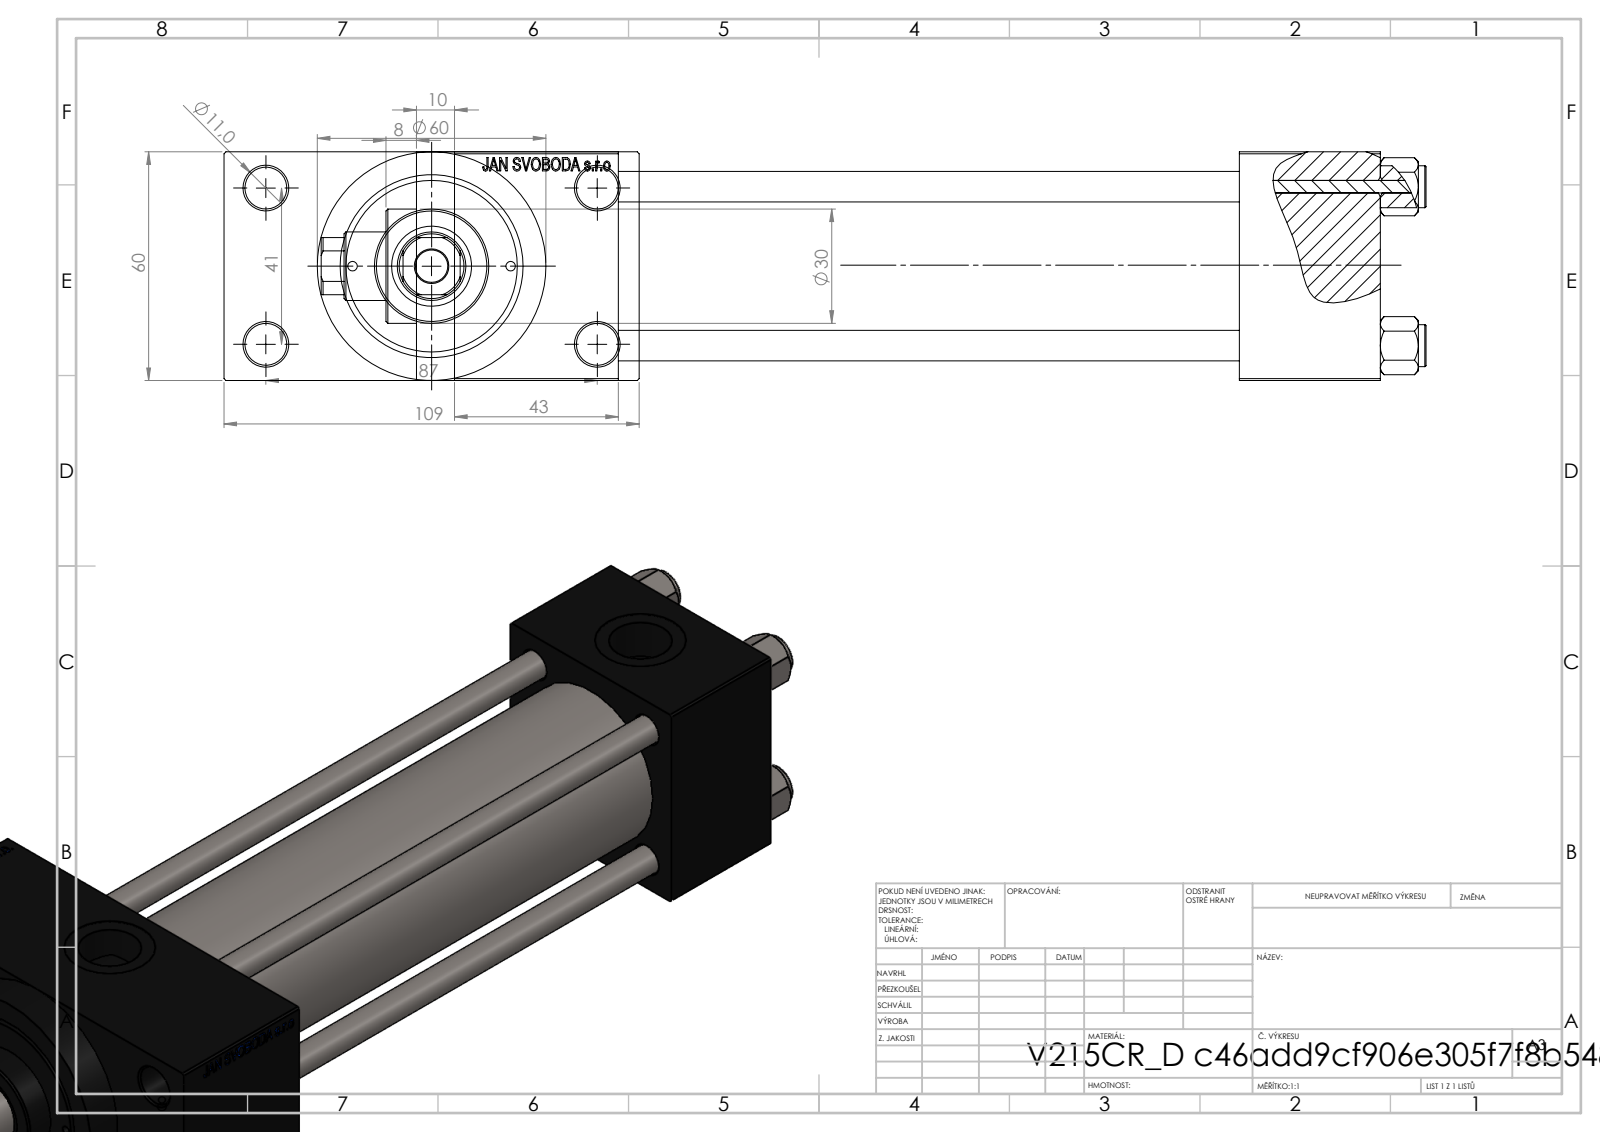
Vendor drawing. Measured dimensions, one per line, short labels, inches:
name: V215CR_VCP_D; V215CR_D_TYCINKA; NUT_M5_D; V215CR_D_Body (+1 more)
written by: SolidWorks 2019 (CONFIG_CONTROL_DESIGN)
unit: in
bodies: 11 solids, 1113 faces (500 planar, 93 cylindrical, 520 other)
size: 11.417 × 4.291 × 2.362
volume: 37.1 in³; area: 257.4 in²
holes: 4× ⌀0.315, 4× ⌀0.433, 2× ⌀0.098, 2× ⌀0.276, 2× ⌀0.656, 2× ⌀0.945, 1× ⌀0.335, 1× ⌀0.709, 1× ⌀0.827, 1× ⌀1.22, 1× ⌀1.575, 1× ⌀1.772
bosses: 4× ⌀0.433, 1× ⌀2.362, 1× ⌀1.811, 1× ⌀1.181
rounds: 1× R0.335
face distances: 2.362, 0.965, 3.327, 6.417, 1.457, 7.874, 9.567, 8.11, 1.693, 4.291
hole spacings: 0.821, 0.892, 1.161, 1.206, 1.642, 1.832, 1.856, 1.893
